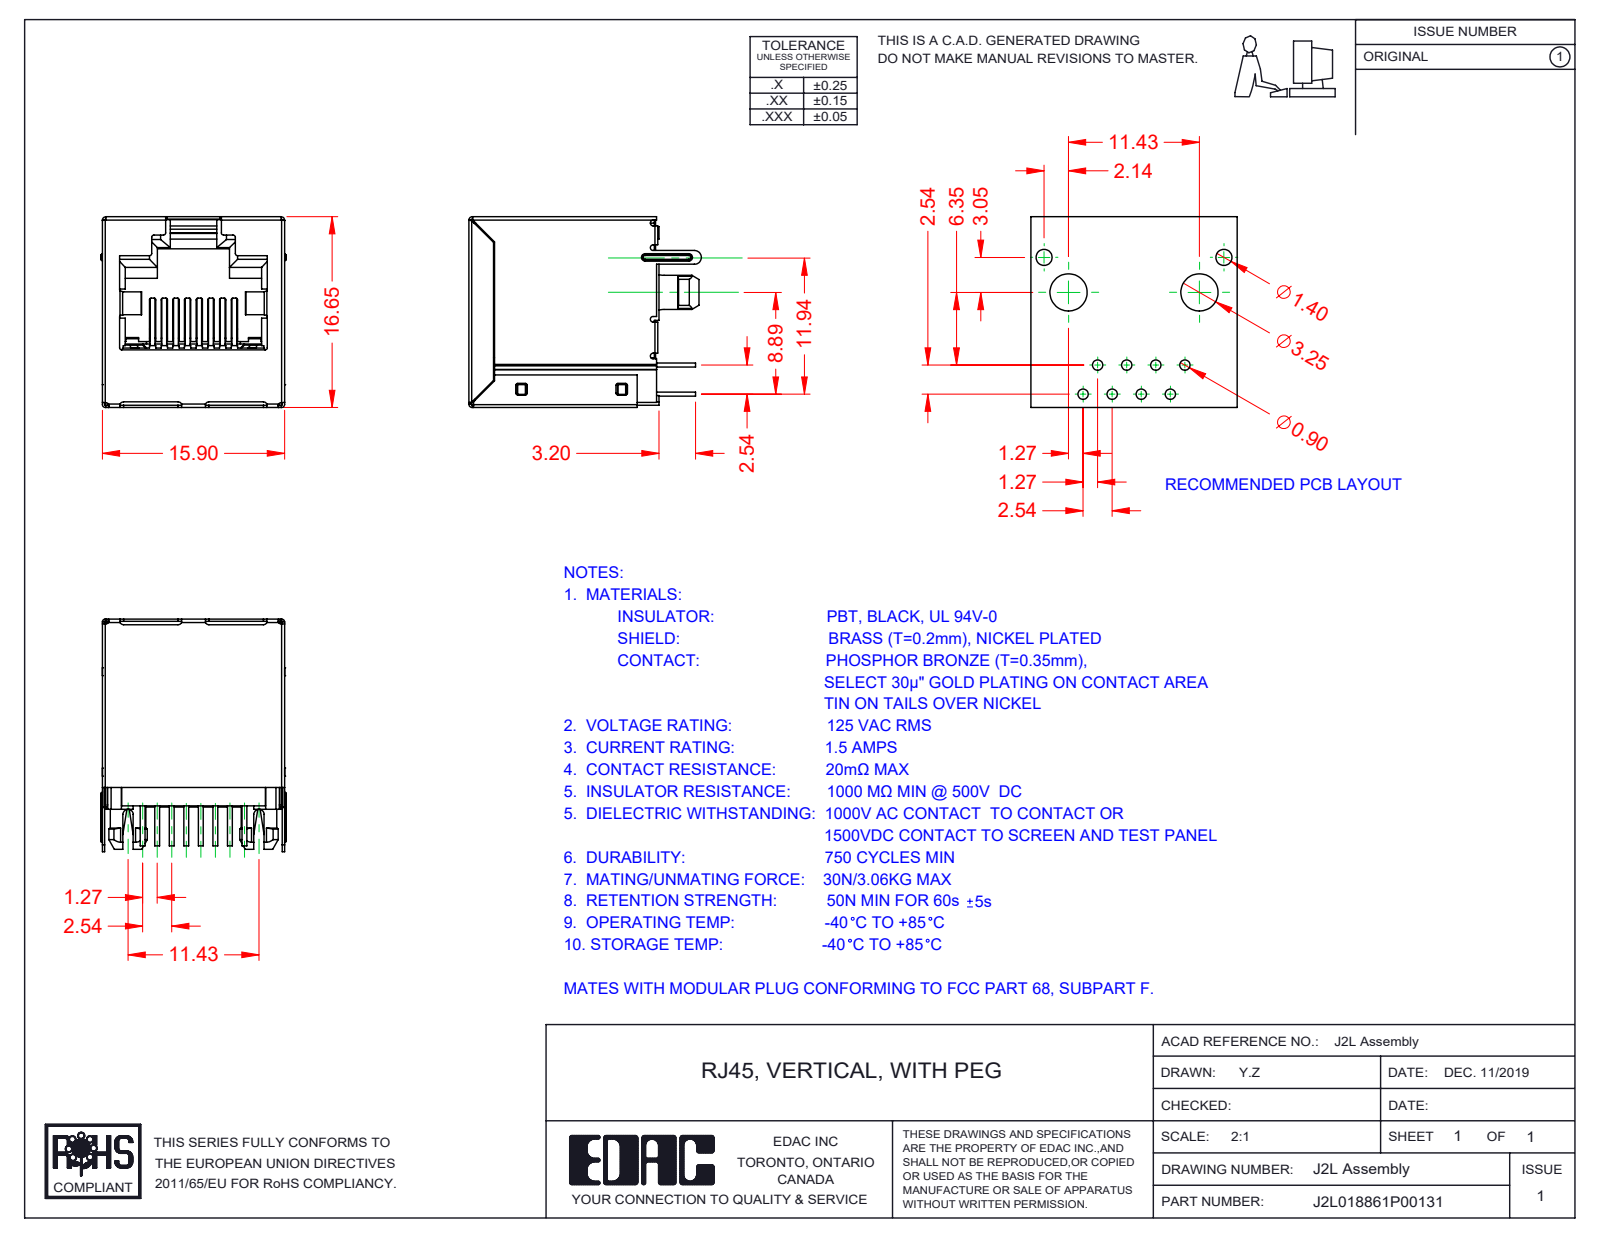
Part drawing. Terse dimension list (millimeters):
name: 2L Shield; 2L Insulator; RJ2L018861P00131; 2L Contacts (+1 more)
written by: SolidWorks 2016 (CONFIG_CONTROL_DESIGN)
unit: mm
bodies: 11 solids, 1125 faces (778 planar, 284 cylindrical, 63 other)
size: 20.3 × 16.65 × 16.2
volume: 2 717 mm³; area: 6 473 mm²
bosses: 2× ⌀3.1, 2× ⌀1.1
rounds: 64× R0.15, 20× R0.25, 16× R0.2, 14× R0.3, 9× R0.35, 8× R0.1, 4× R0.28, 3× R0.5
face distances: 15.45, 15.7, 16.45, 16.2, 16.4, 15.65, 16.25, 15.9, 15.5, 1.2
